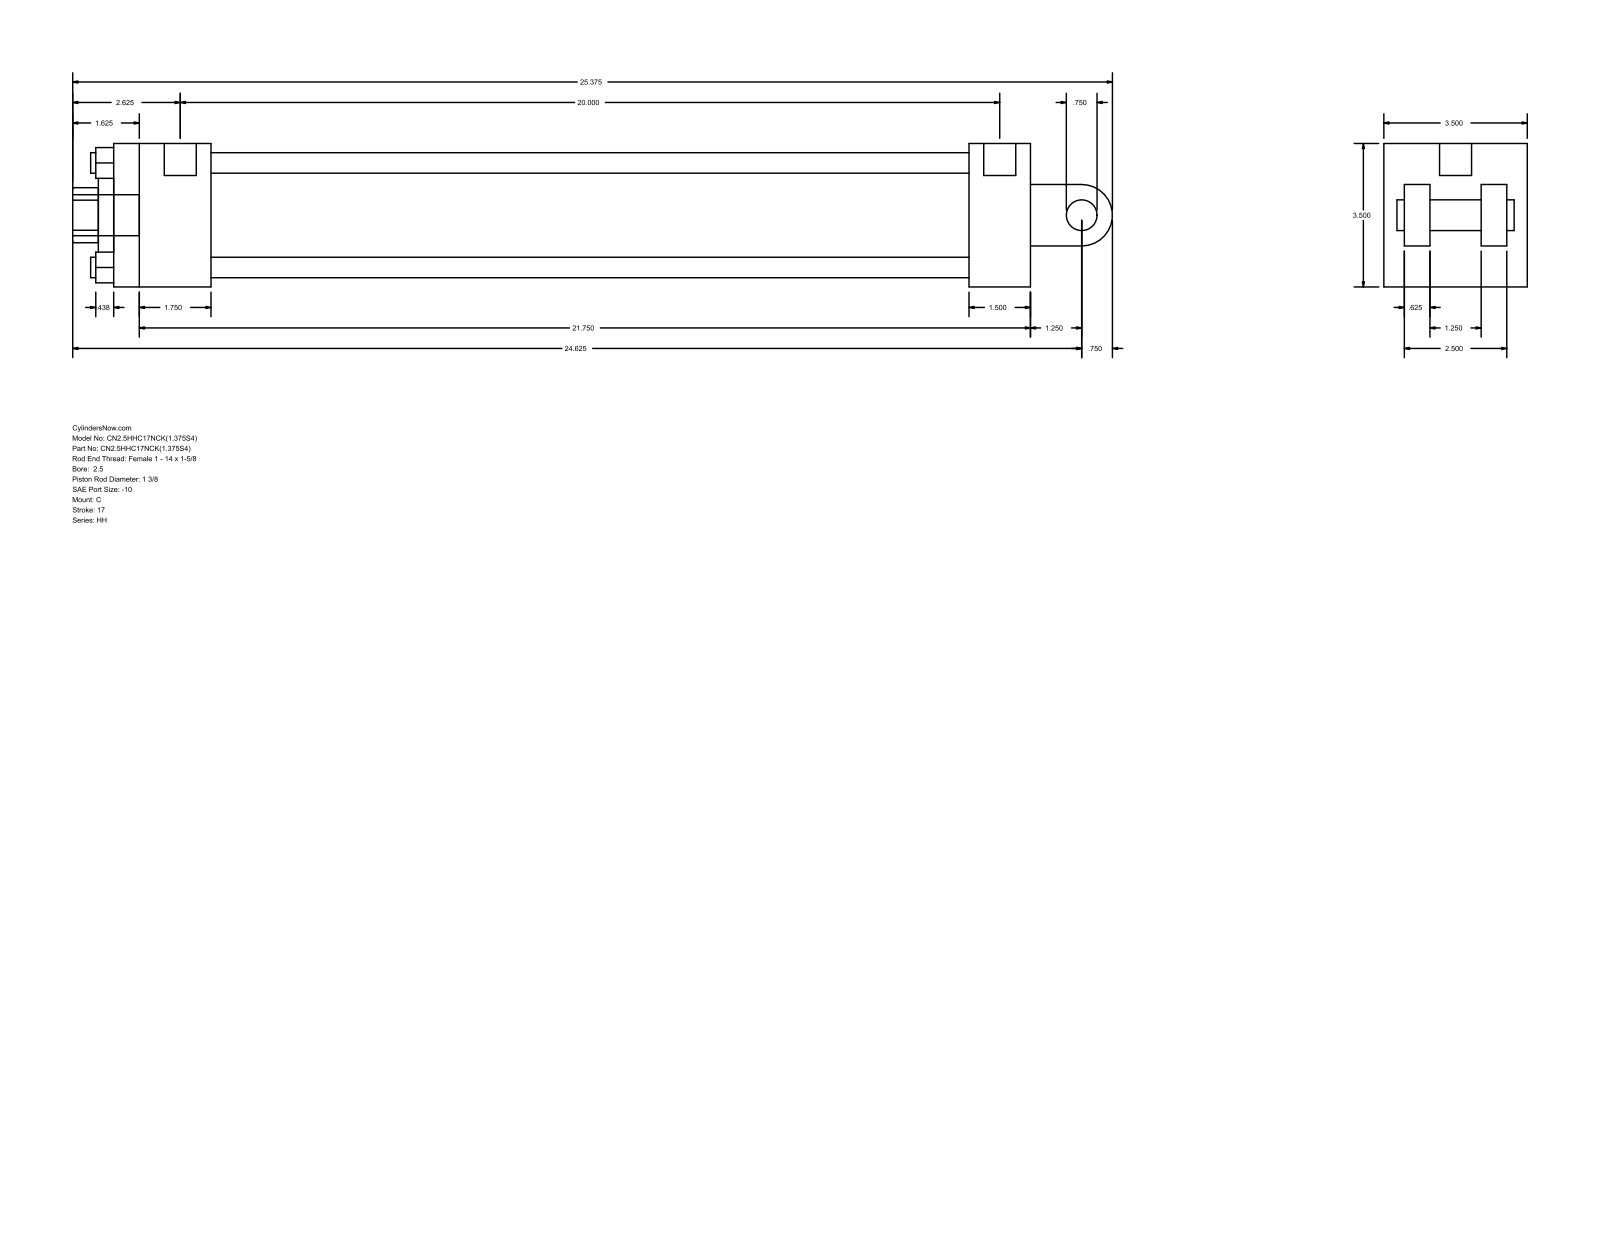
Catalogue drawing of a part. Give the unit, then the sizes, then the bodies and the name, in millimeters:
Units: millimetres
Overall size (bounding box): 644.52 × 88.9 × 88.9
Round holes (diameter × count): ⌀12.7 ×4, ⌀5.56 ×2, ⌀19.84 ×1, ⌀34.92 ×1, ⌀50.8 ×1, ⌀73.03 ×1
Round bosses / shafts (diameter × count): ⌀5.56 ×2, ⌀25.4 ×1, ⌀19.84 ×1, ⌀19.05 ×1
Partial cylindrical surfaces — rounded edges, fillets, slot ends (radius × count): R17.06 ×1, R19.05 ×1
Main face-to-face distances: 88.9, 568.33, 63.5, 15.87, 12.7, 530.22, 38.11, 60.32, 469.9, 508.01
Hole centre spacings: 45.79, 64.76, 91.58, 1.59
Bodies: 0 solids, 99 faces (70 planar, 29 cylindrical, 0 other)
Part name (STEP PRODUCT): HH_C__0250_1.375
STEP written by: GSSL Pune (CONFIG_CONTROL_DESIGN)
